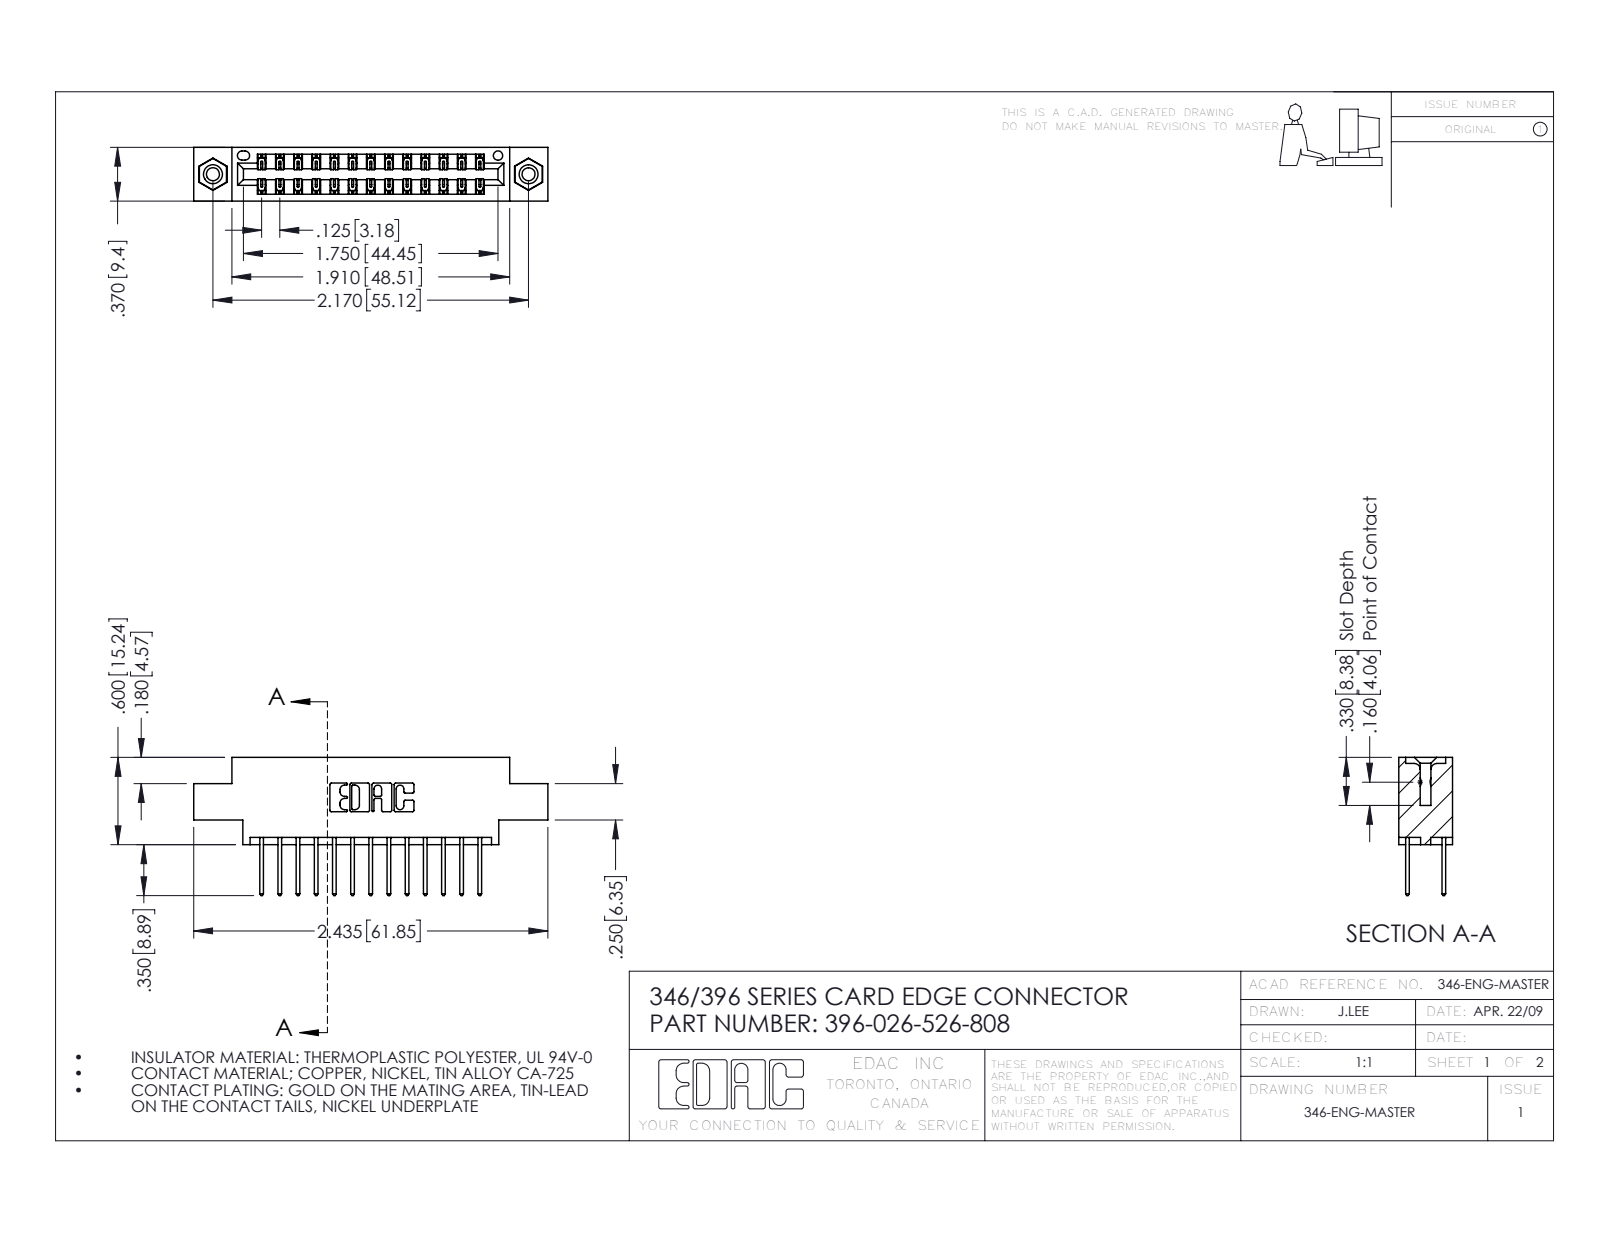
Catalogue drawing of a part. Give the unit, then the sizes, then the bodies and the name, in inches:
Units: inches
Overall size (bounding box): 2.435 × 0.95 × 0.37
Round holes (diameter × count): ⌀0.089 ×2, ⌀0.125 ×2, ⌀0.156 ×2, ⌀0.064 ×1
Round bosses / shafts (diameter × count): ⌀0.155 ×2
Partial cylindrical surfaces — rounded edges, fillets, slot ends (radius × count): R0.006 ×39, R0.01 ×26, R0.01 ×22, R0.007 ×6, R0.031 ×6, R0.026 ×3, R0.014 ×2, R0.022 ×2
Main face-to-face distances: 0.048, 0.322, 0.25, 0.37, 0.072, 0.298, 0.025, 0.275, 0.222, 0.148
Hole centre spacings: 0.246, 1.964, 2.17
Volume: 0.347 in³ · Surface area: 12.02 in²
Bodies: 29 solids, 1538 faces (1022 planar, 500 cylindrical, 16 other)
Part name (STEP PRODUCT): 345-250-001_345-250-003-102; 346 Part_0.170 Offset - 0.156 Dia-TI; 396-026-526-808; 345-292-001_345-293-126
STEP written by: SolidWorks 2016 (CONFIG_CONTROL_DESIGN)
